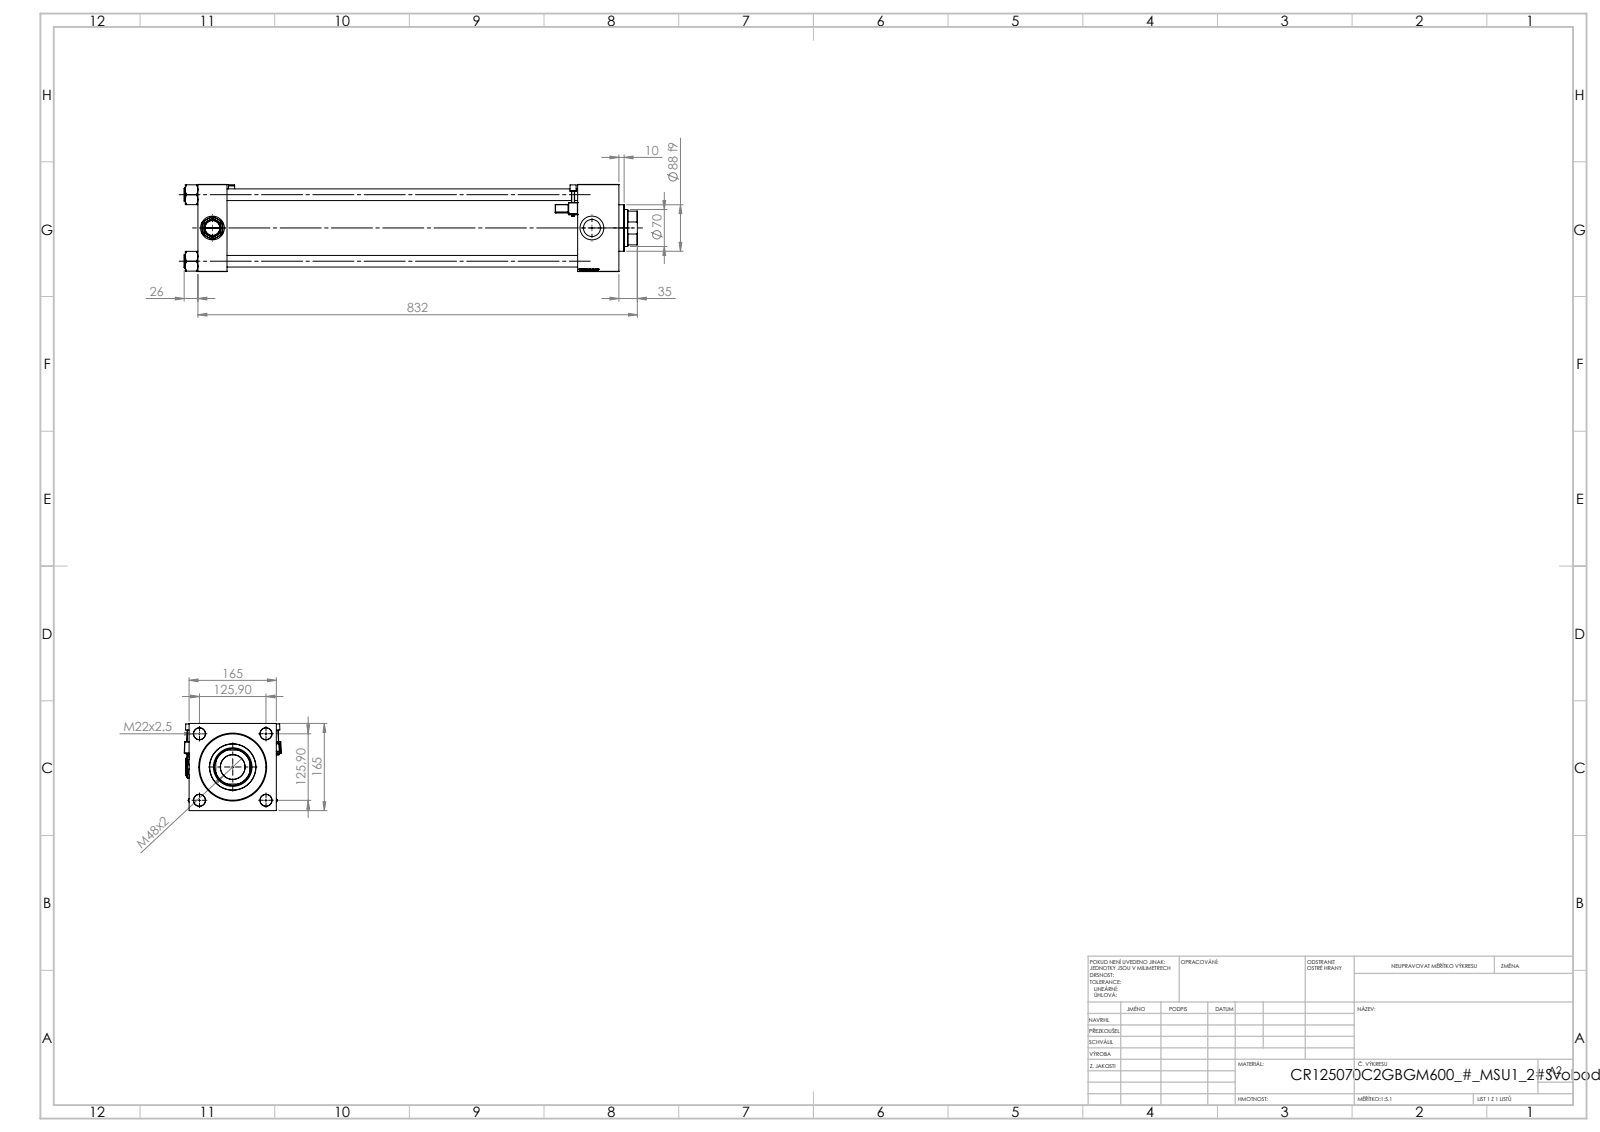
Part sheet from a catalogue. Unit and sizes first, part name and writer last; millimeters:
Units: millimetres
Overall size (bounding box): 858 × 183.5 × 165
Round holes (diameter × count): ⌀22 ×4, ⌀7 ×2, ⌀32.24 ×2, ⌀45 ×2, ⌀46.5 ×1, ⌀70 ×1, ⌀73 ×1, ⌀96 ×1, ⌀125 ×1, ⌀125.5 ×1
Round bosses / shafts (diameter × count): ⌀25 ×4, ⌀6 ×2, ⌀131 ×1, ⌀88 ×1
Partial cylindrical surfaces — rounded edges, fillets, slot ends (radius × count): R0.5 ×48, R1 ×2, R2.5 ×2, R4 ×2, R34 ×1
Main face-to-face distances: 165, 55, 742, 797, 78, 719, 664, 768.3, 713.3, 49.3
Hole centre spacings: 89.02, 125.9, 178.05, 718.5
Volume: 8 455 000 mm³ · Surface area: 1 284 000 mm²
Bodies: 14 solids, 1404 faces (656 planar, 154 cylindrical, 594 other)
Part name (STEP PRODUCT): NUT_M5_C; V215_VC_A; V215CR_C_TYCINKA; V215CR_MSU (+3 more)
STEP written by: SolidWorks 2019 (CONFIG_CONTROL_DESIGN)
